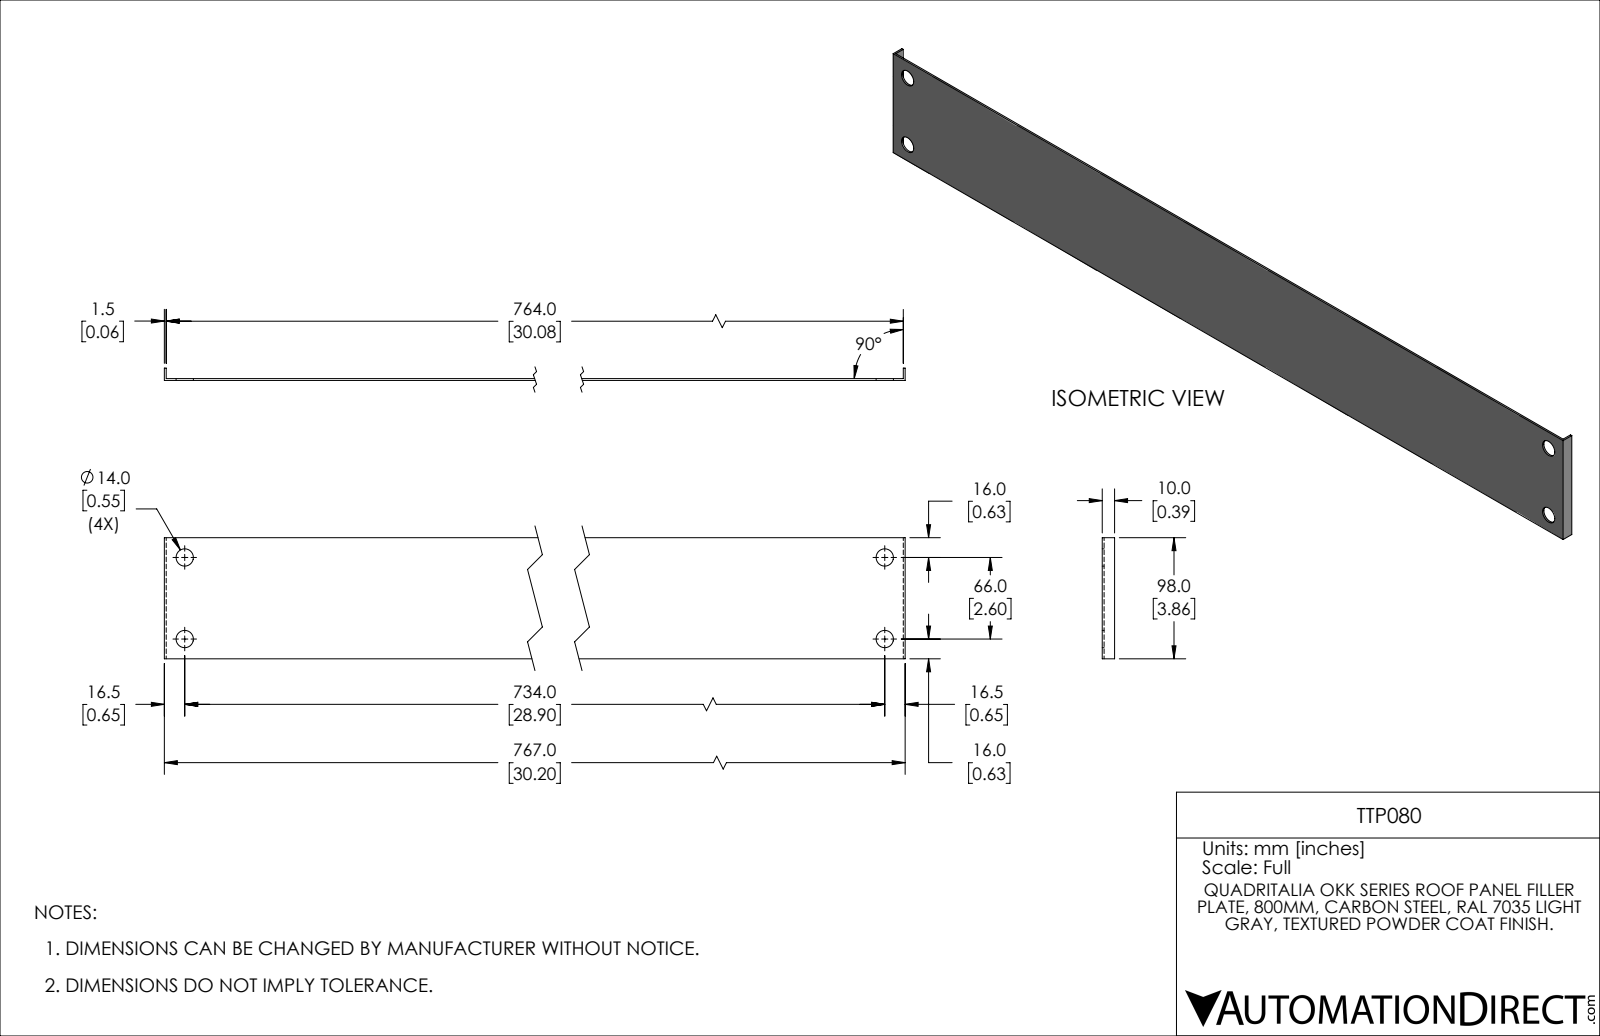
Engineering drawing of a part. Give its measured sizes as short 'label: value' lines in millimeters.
name: TTP080
written by: SolidWorks 2021 (CONFIG_CONTROL_DESIGN)
unit: mm
bodies: 1 solid, 14 faces (10 planar, 4 cylindrical, 0 other)
size: 767 × 98 × 10
volume: 114 300 mm³; area: 155 400 mm²
holes: 4× ⌀14
face distances: 1.5, 765.5, 98, 767, 764, 8.5, 10
hole spacings: 66, 734, 737
